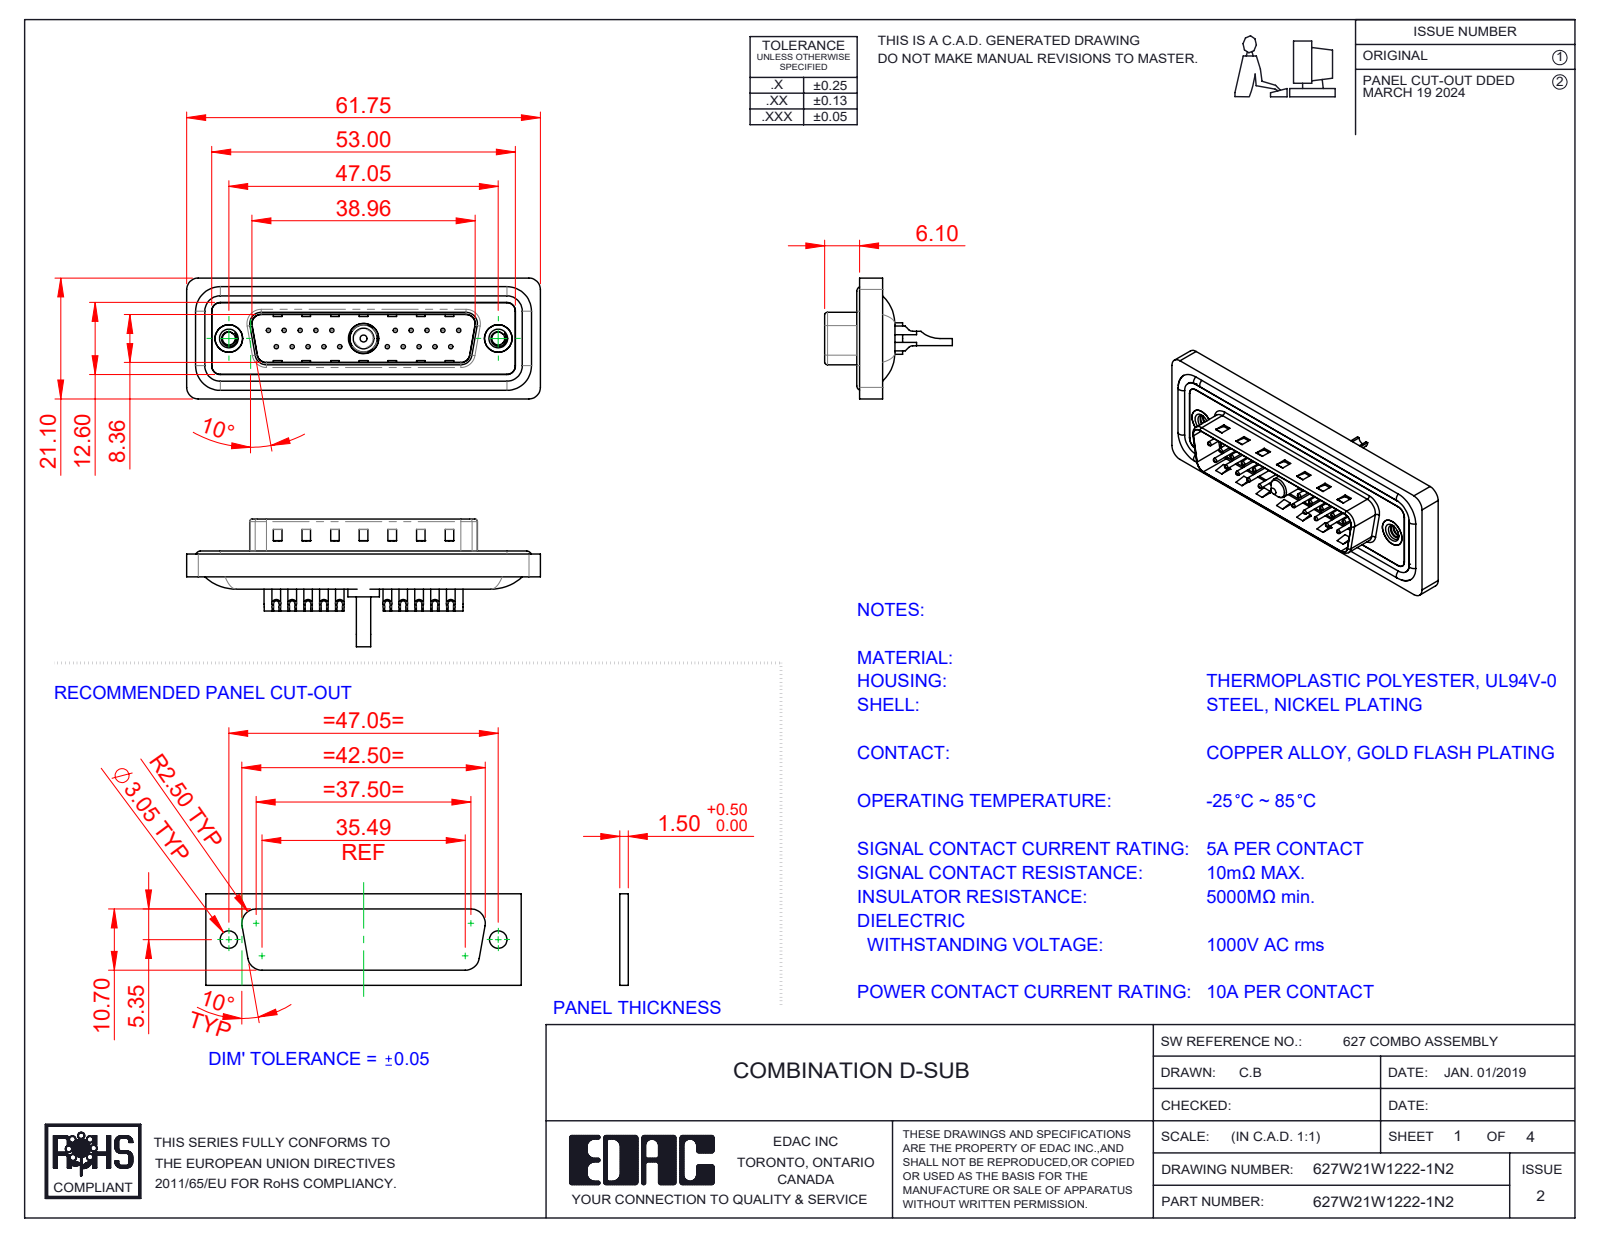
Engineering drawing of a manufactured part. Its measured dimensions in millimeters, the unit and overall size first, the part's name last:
Units: millimetres
Overall size (bounding box): 61.75 × 22.3 × 21.1
Round holes (diameter × count): ⌀0.75 ×20, ⌀1 ×20, ⌀1.6 ×20, ⌀2 ×20, ⌀2.26 ×2, ⌀4 ×2, ⌀4.8 ×2, ⌀5 ×2, ⌀1.7 ×1, ⌀4.85 ×1, ⌀5.3 ×1
Round bosses / shafts (diameter × count): ⌀1.5 ×20, ⌀1.6 ×4, ⌀4.9 ×2, ⌀5.5 ×1, ⌀5.2 ×1, ⌀4.75 ×1, ⌀3.75 ×1, ⌀3.6 ×1
Partial cylindrical surfaces — rounded edges, fillets, slot ends (radius × count): R1.5 ×22, R2 ×18, R0.5 ×8, R1.6 ×8, R1 ×6, R0.25 ×4, R0.6 ×4, R0.65 ×4
Main face-to-face distances: 0.4, 1.5, 1.1, 1.6, 0.5, 3.1, 2.9, 4.1, 0.82, 9.58
Hole centre spacings: 3.16, 2.77, 5.54, 8.31, 5.04, 19.39, 20.97, 22.16
Volume: 7 226 mm³ · Surface area: 12 160 mm²
Bodies: 29 solids, 1268 faces (401 planar, 530 cylindrical, 337 other)
Part name (STEP PRODUCT): 627Combo Contact Row 1_22; 627Combo Shell Rear_25 Contacts; 627Combo Shell Front_25 Contacts; 627W21W1222-1N2 (+5 more)
STEP written by: SolidWorks 2023 (CONFIG_CONTROL_DESIGN)
